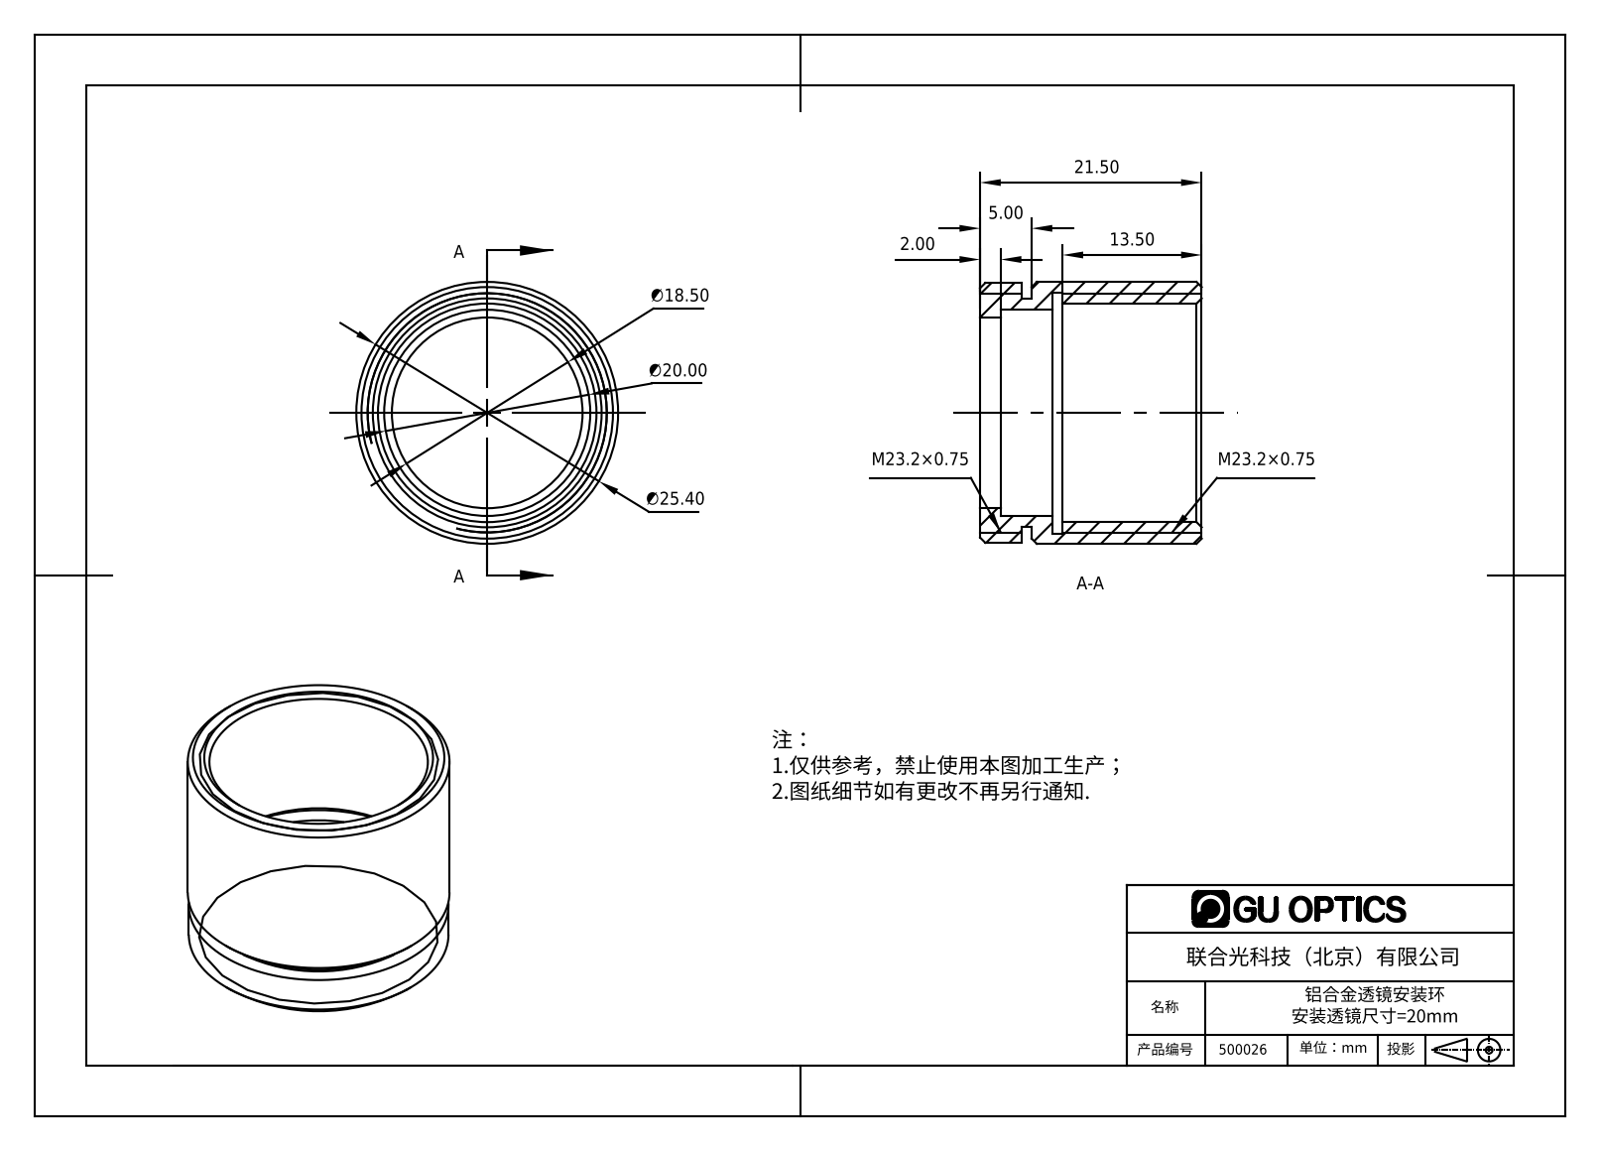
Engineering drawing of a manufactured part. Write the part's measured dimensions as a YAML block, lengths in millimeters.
part_name: "500026"
step_written_by: "SolidWorks 2016 (AUTOMOTIVE_DESIGN)"
units: millimeters
bodies: {solids: 1, faces: 29, planar: 7, cylindrical: 14, other: 8}
overall_size: [25.4, 25.4, 21.5]
volume: 3401
surface_area: 3869
round_holes:
  - {diameter: 18.5, count: 1}
  - {diameter: 20, count: 1}
  - {diameter: 21.2, count: 1}
  - {diameter: 23.4, count: 1}
round_bosses_or_shafts:
  - {diameter: 25.4, count: 1}
  - {diameter: 25.2, count: 1}
  - {diameter: 22.2, count: 1}
face_to_face_distances: [3, 4, 2, 1, 5, 7, 21.5, 17.5, 16.5, 14.5]
